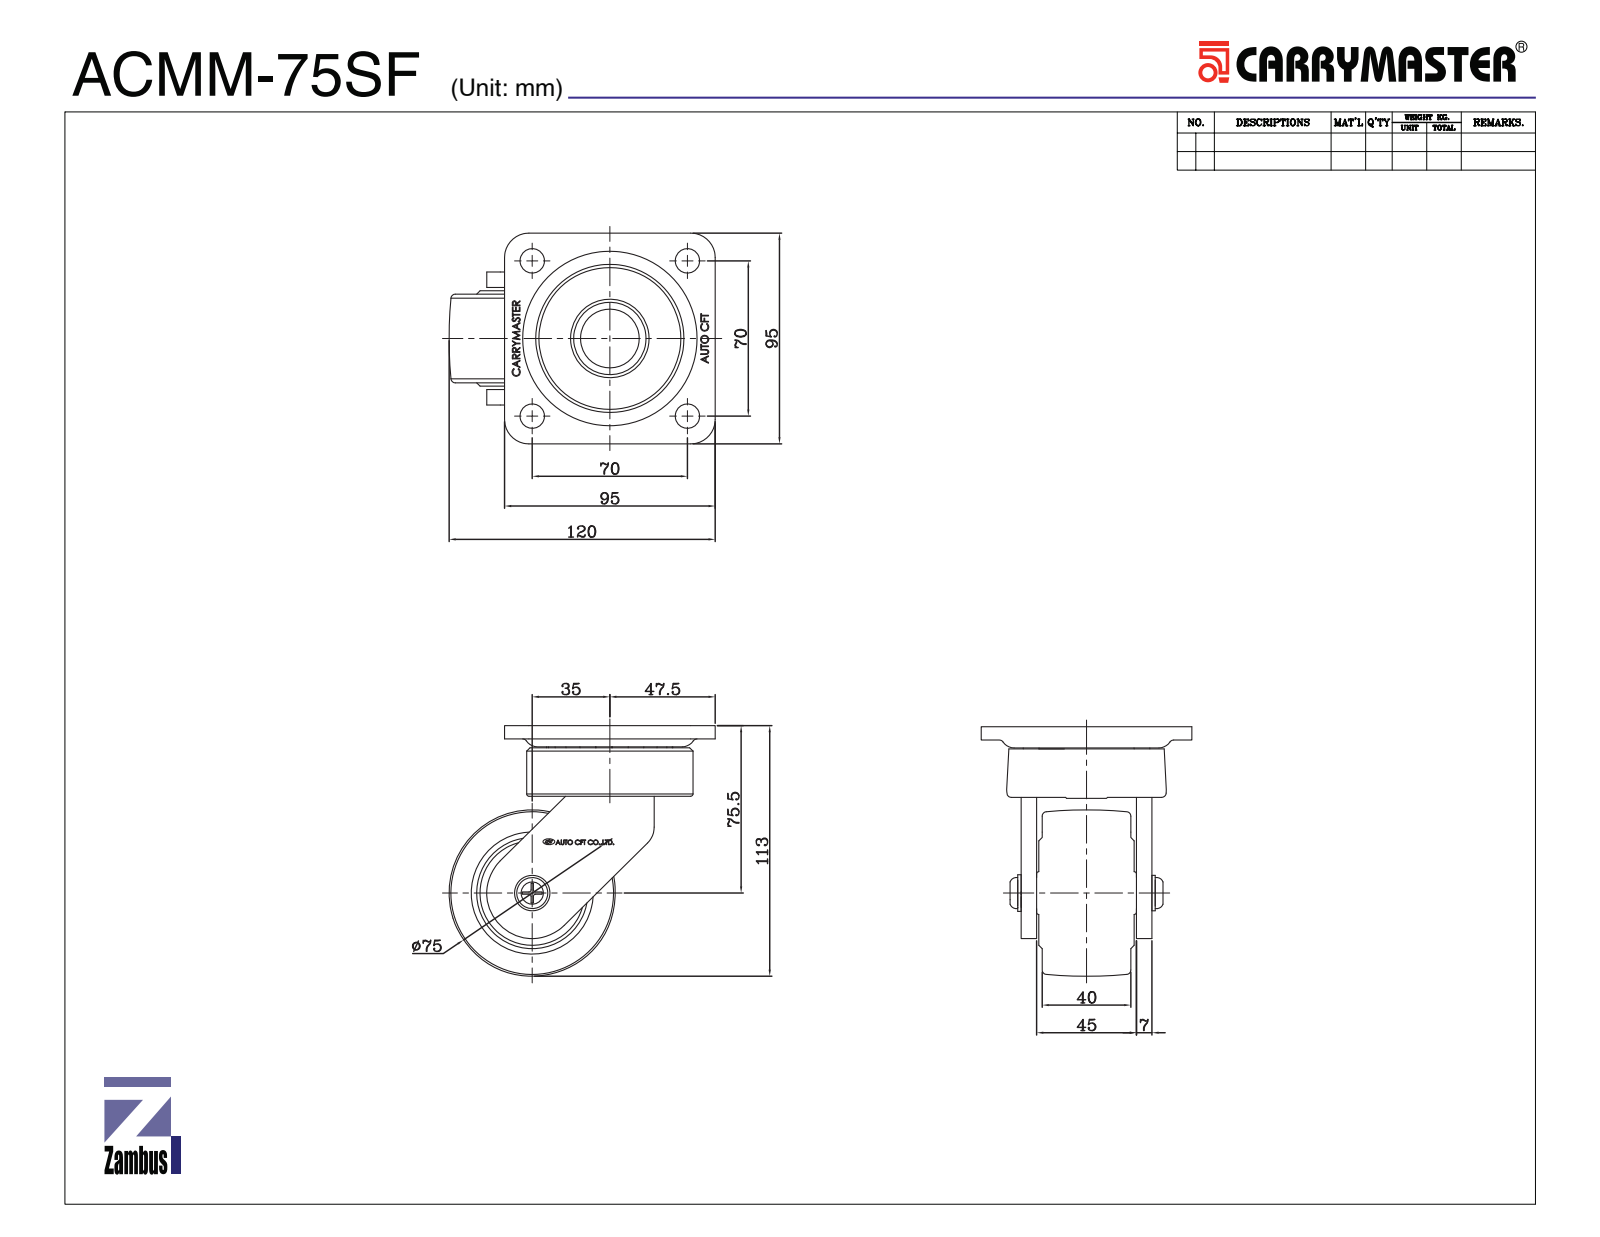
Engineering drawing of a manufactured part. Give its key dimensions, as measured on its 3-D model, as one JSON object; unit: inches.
{"part_name": "ACMM-75SF", "step_written_by": "SolidWorks 2015 (CONFIG_CONTROL_DESIGN)", "units": "inches", "bodies": {"solids": 9, "faces": 359, "planar": 152, "cylindrical": 115, "other": 92}, "overall_size": [4.724, 4.449, 3.74], "volume_in3": 19.4, "surface_area_in2": 128.3, "round_holes": [[0.433, 4], [0.268, 1], [0.484, 1], [0.689, 1], [1.043, 1], [1.224, 1], [1.457, 1], [1.654, 1], [2.441, 1]], "round_bosses_or_shafts": [[1.496, 1], [0.984, 1], [0.787, 1], [0.63, 1], [0.551, 1], [0.472, 1], [0.315, 1]], "partial_cylinders_radius": [[0.079, 12], [0.197, 4], [0.433, 4], [0.472, 1], [0.571, 1], [0.787, 1], [1.417, 1]], "face_to_face_distances": [0.276, 2.047, 0.098, 0.236, 0.374, 1.949, 1.673, 0.039, 1.018, 1.254], "hole_center_spacings": [1.949, 2.756, 3.897]}
